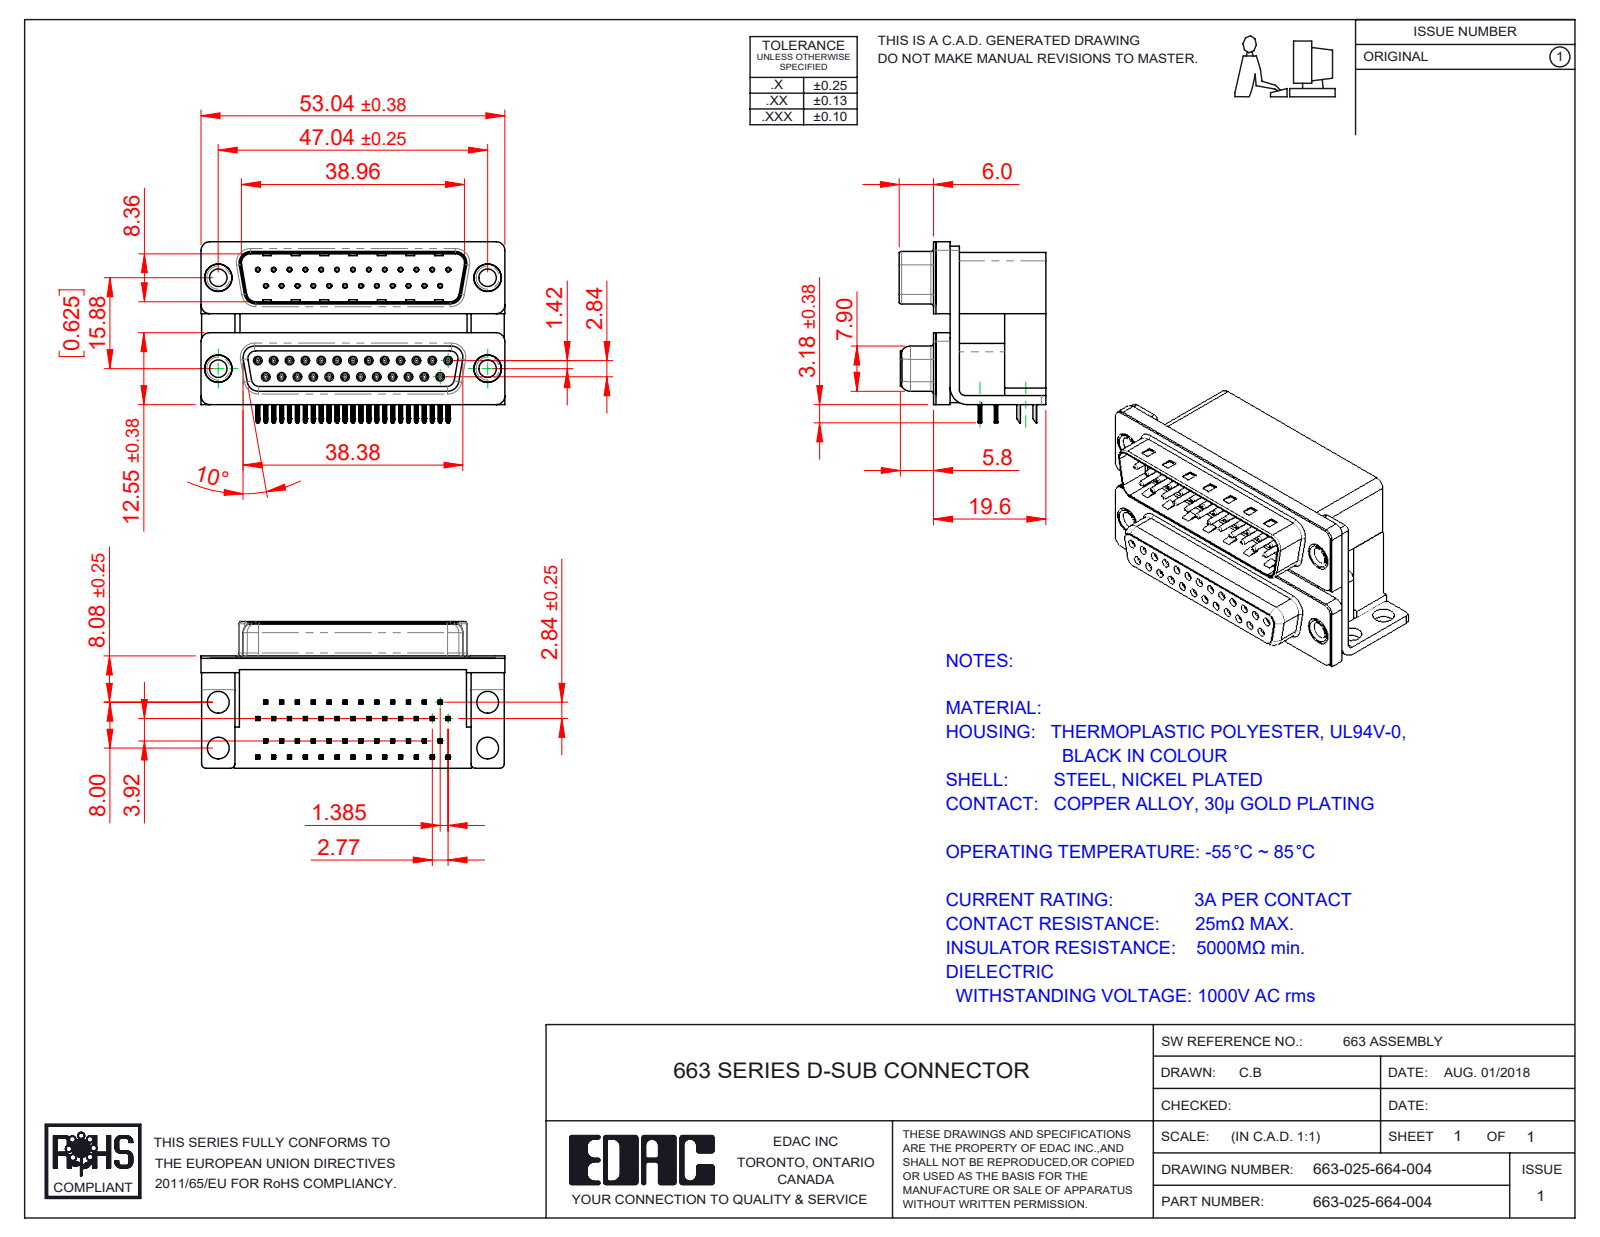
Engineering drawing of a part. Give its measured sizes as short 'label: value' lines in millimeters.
name: 663 Housing Lower_25 Contacts; 663 Thru Hole Rivet; 663 Shell Receptacle_25 Contacts; 663 Housing Upper_25 Contacts L (+8 more)
written by: SolidWorks 2020 (CONFIG_CONTROL_DESIGN)
unit: mm
bodies: 61 solids, 6119 faces (3257 planar, 1507 cylindrical, 1355 other)
size: 53.04 × 31.61 × 25.6
volume: 21 580 mm³; area: 22 934 mm²
holes: 50× ⌀0.8, 25× ⌀0.35, 25× ⌀0.9, 4× ⌀3.05, 4× ⌀3.5, 4× ⌀3.8, 4× ⌀4, 4× ⌀4.8, 4× ⌀5
bosses: 25× ⌀1.2, 25× ⌀0.75, 4× ⌀4.9, 4× ⌀4.75, 4× ⌀3.85
rounds: 200× R0.1, 100× R0.15, 100× R0.25, 50× R0.12, 50× R0.35, 25× R0.34, 13× R1.5, 12× R0.28
face distances: 0.4, 19.2, 7.2, 12, 10.7, 16.7, 9.5, 2.5, 15.53, 26.23
hole spacings: 3.16, 2.77, 5.54, 11.08, 8.31, 5.03, 13.85, 7.48
